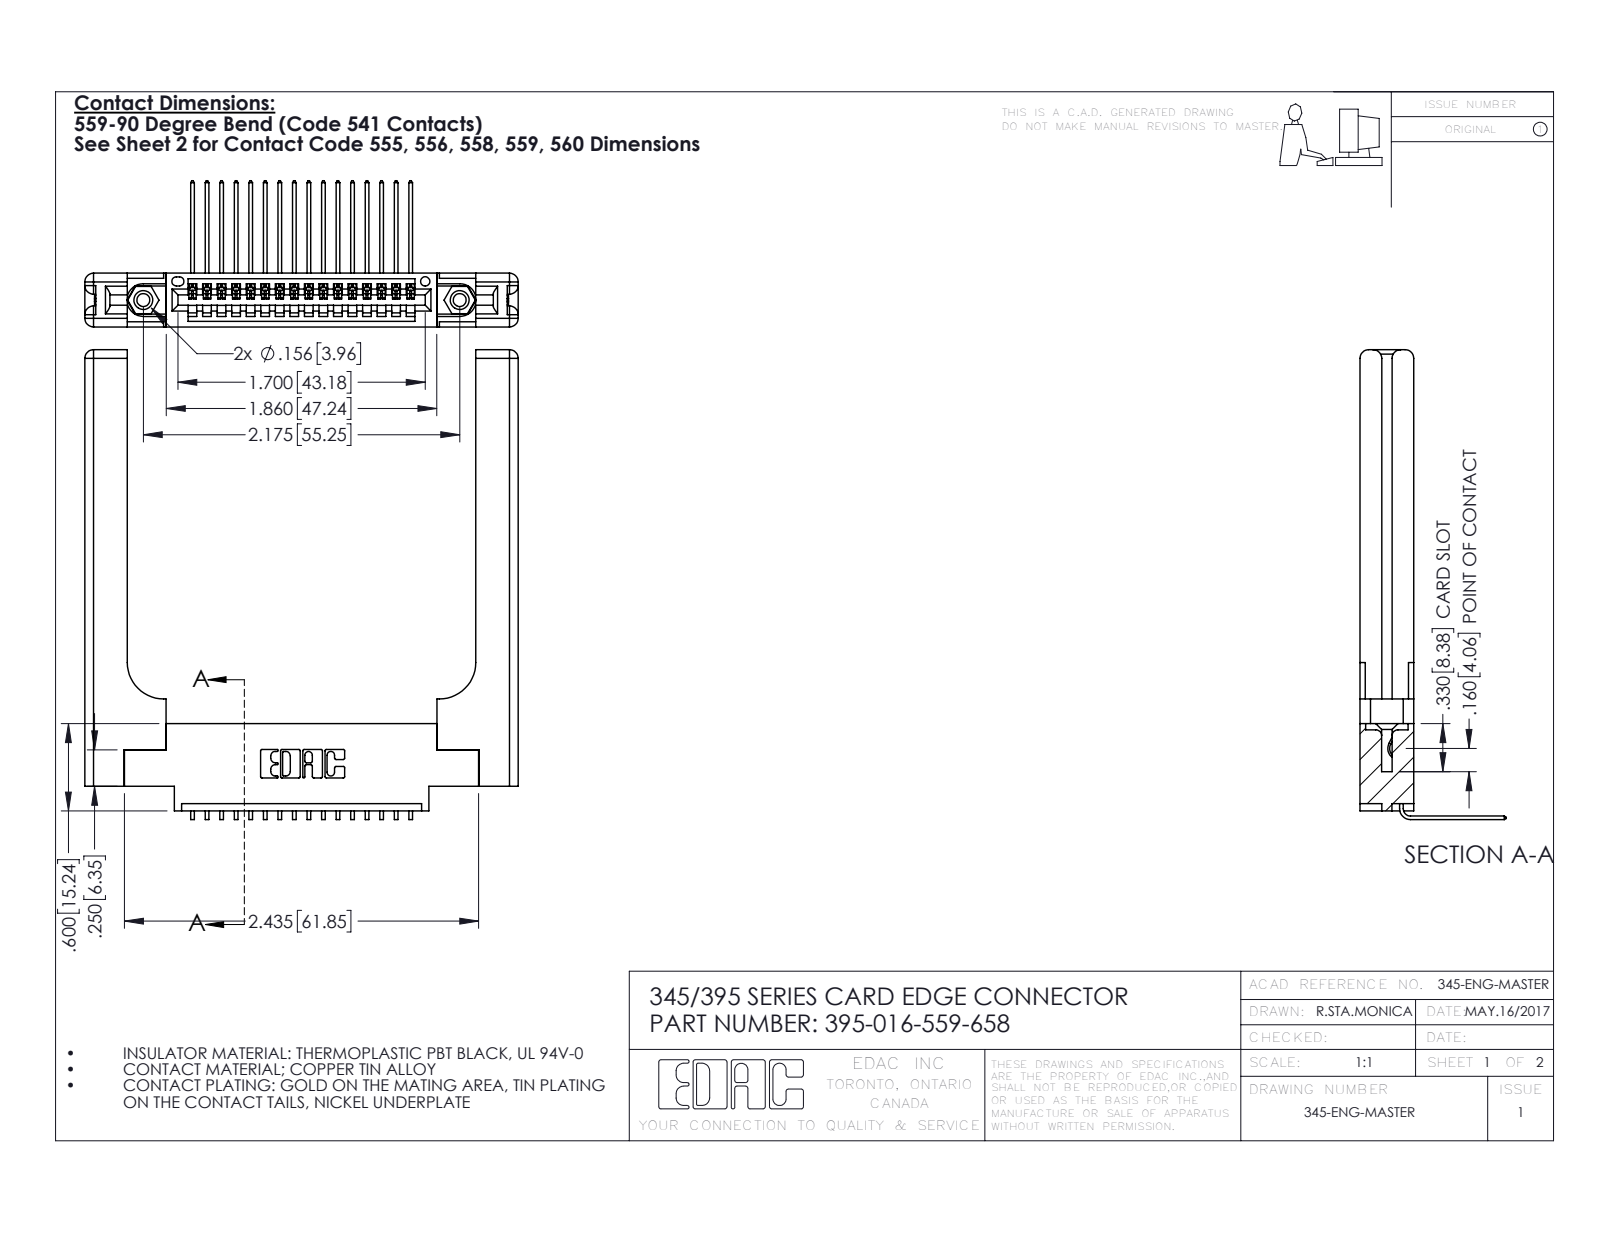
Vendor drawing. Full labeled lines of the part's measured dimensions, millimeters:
Part name (STEP PRODUCT): 345 Part_0.170 Offset - 0.156 Dia-TH; 345-220-058_345-220-058; 345-250-001_345-250-001-102; 345-292-001_558 559 Tail - 1 (+1 more)
STEP written by: SolidWorks 2016 (CONFIG_CONTROL_DESIGN)
Units: millimetres
Bodies: 21 solids, 1346 faces (904 planar, 382 cylindrical, 60 other)
Overall size (bounding box): 82 × 75.7 × 25.5
Volume: 15 400 mm³ · Surface area: 14 580 mm²
Round holes (diameter × count): ⌀2.3 ×2, ⌀3.2 ×2, ⌀4 ×2, ⌀1.6 ×1
Round bosses / shafts (diameter × count): ⌀3.9 ×2
Partial cylindrical surfaces — rounded edges, fillets, slot ends (radius × count): R0.2 ×32, R0.3 ×22, R1.5 ×16, R0.2 ×6, R0.8 ×6, R0.7 ×3, R0.8 ×2, R0.8 ×2
Main face-to-face distances: 9.4, 1.8, 7.6, 3.8, 3.8, 2, 5.6, 3, 3.1, 2.5
Hole centre spacings: 6.9, 49.3, 55.2
